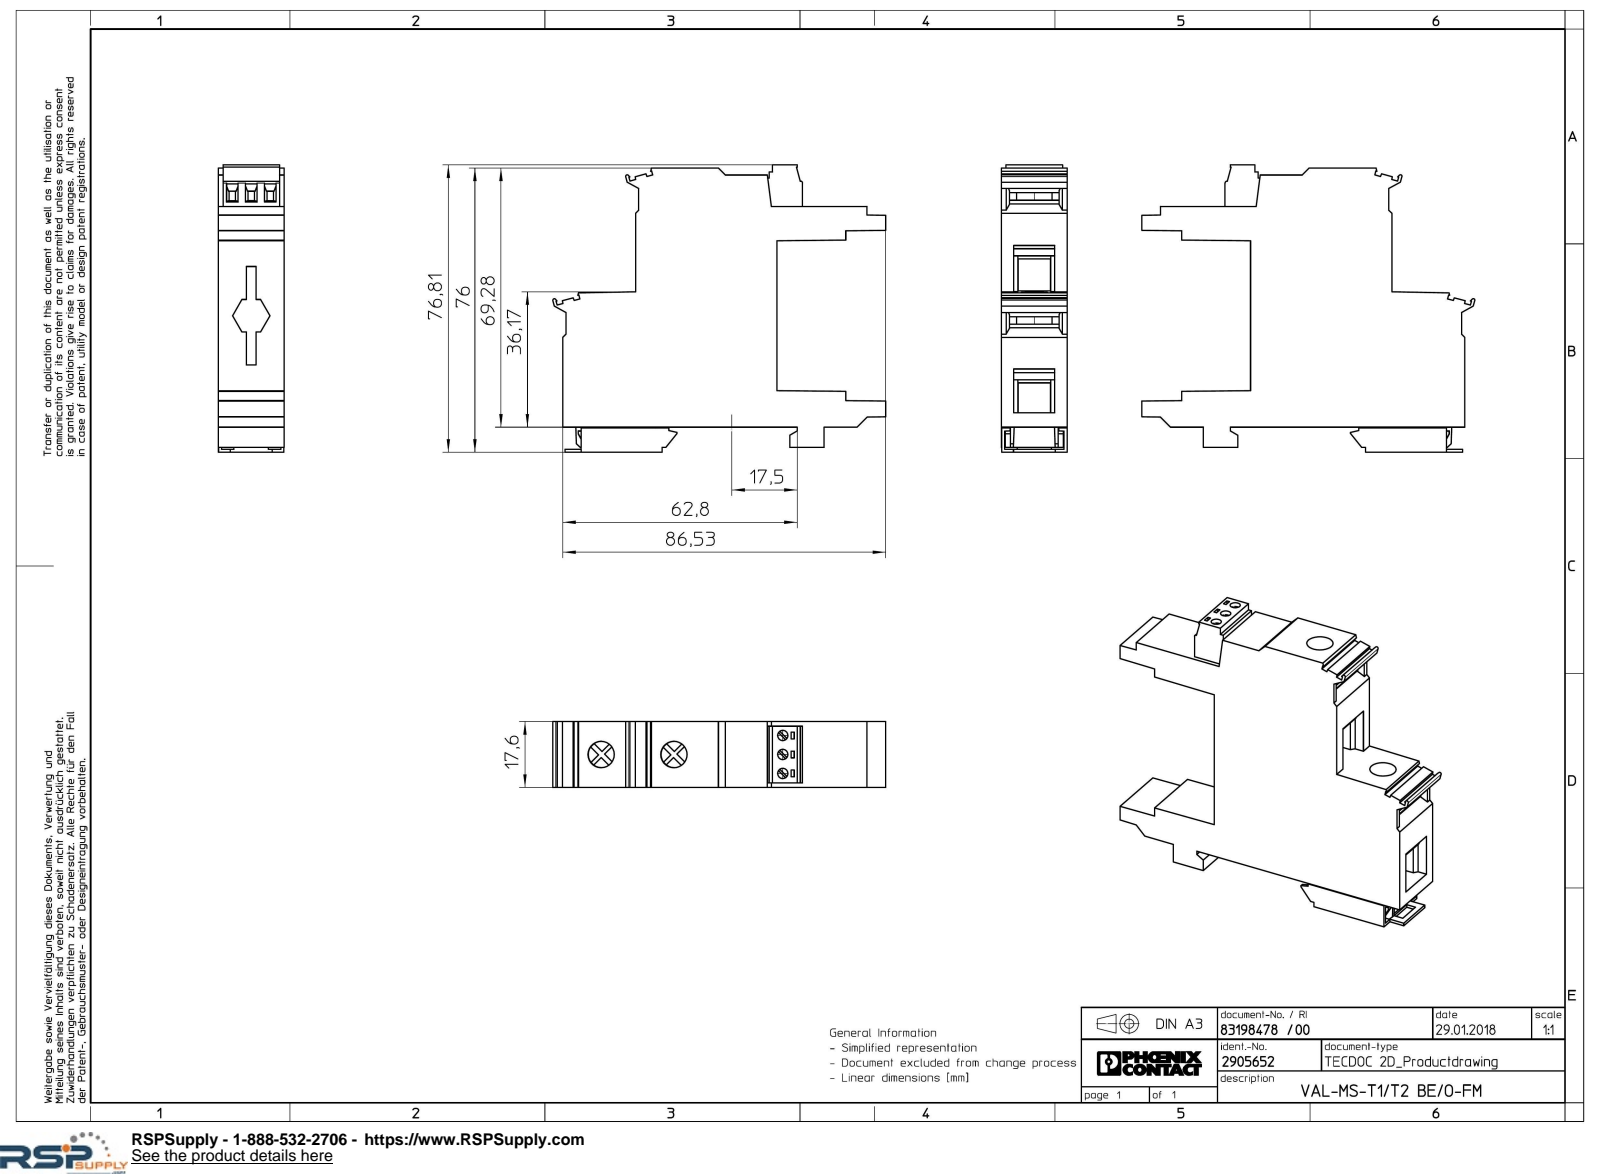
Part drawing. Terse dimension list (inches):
name: VAL_MS_T1_T2_BE_O_FM-select
written by: Creo Elements/Direct Modeling 18.1I 14-Aug-2016 (C) Parametric Technology GmbH (AUTOMOTIVE_DESIGN)
unit: in
bodies: 1 solid, 315 faces (298 planar, 17 cylindrical, 0 other)
size: 3.512 × 3.024 × 0.693
volume: 3.985 in³; area: 30.03 in²
holes: 3× ⌀0.108, 2× ⌀0.278
bosses: 2× ⌀0.374
rounds: 2× R0.016, 1× R0.02
face distances: 0.693, 0.031, 0.098, 1.305, 0.079, 2.322, 0.265, 2.587, 0.11, 0.155
hole spacings: 0.2, 0.4, 0.79
